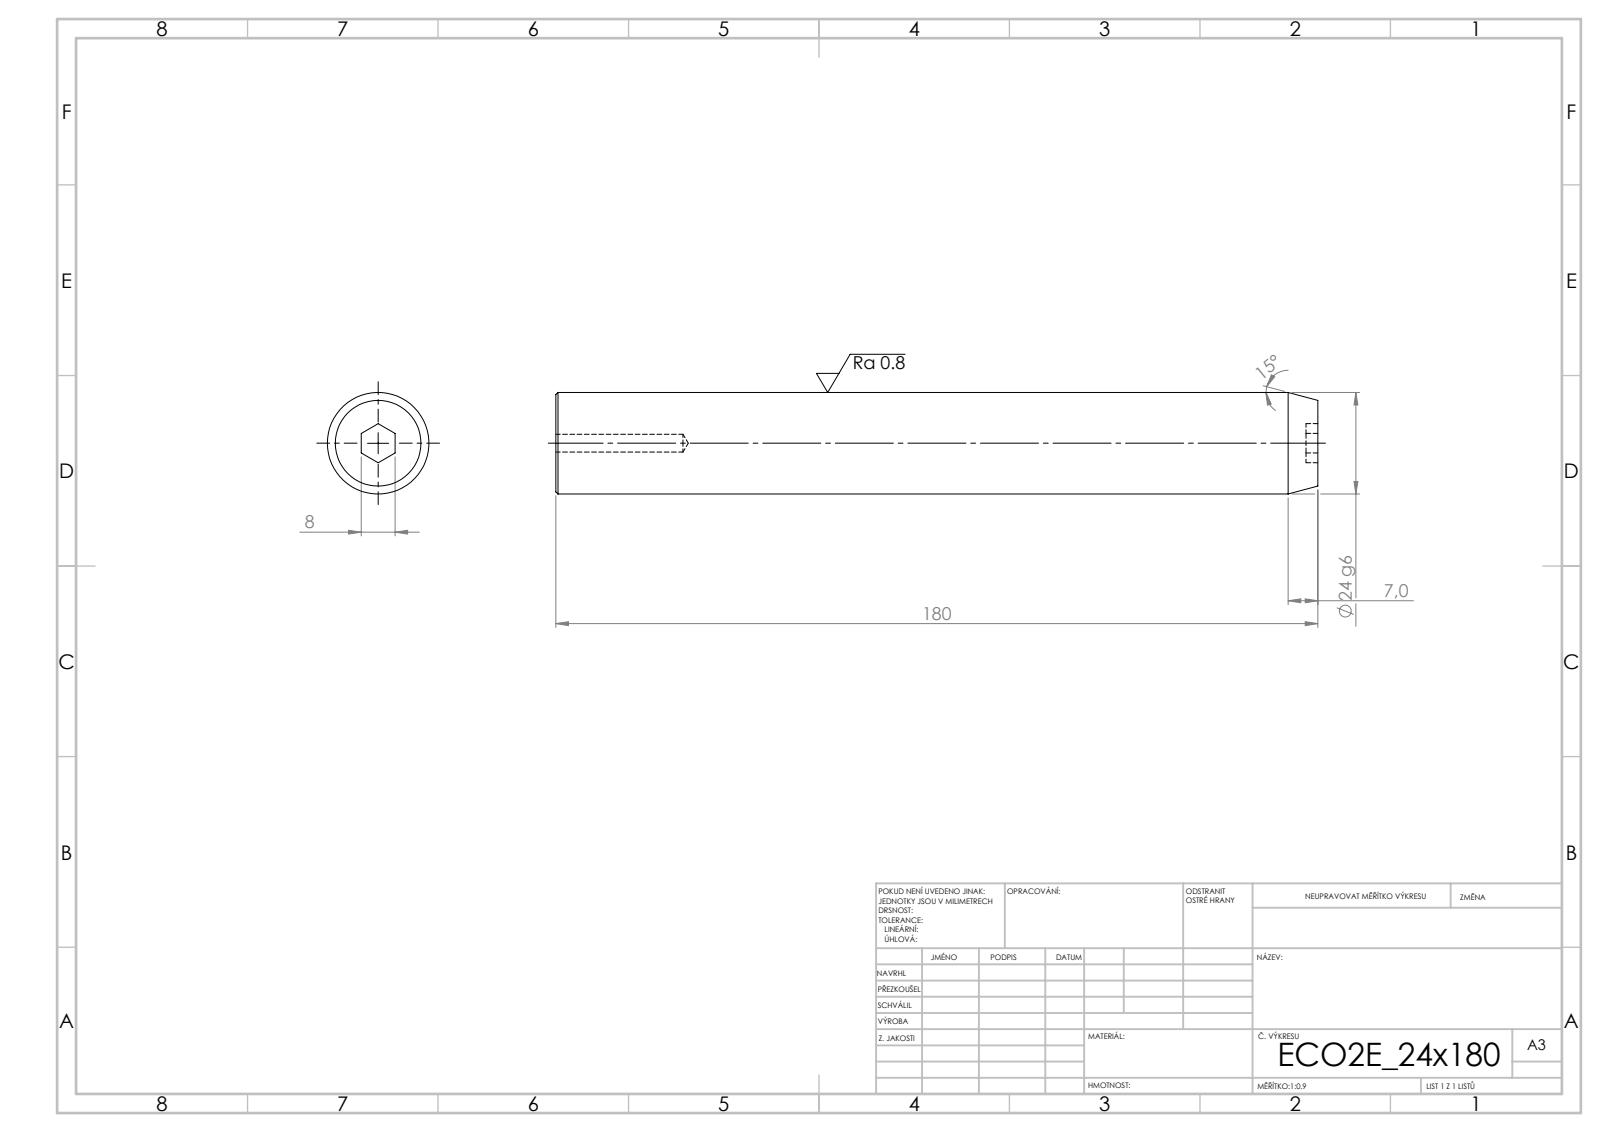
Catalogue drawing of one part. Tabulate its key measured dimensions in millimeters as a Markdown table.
| quantity | value |
| --- | --- |
| STEP written by | SolidWorks 2019 (CONFIG_CONTROL_DESIGN) |
| units | millimeters |
| bodies | 1 solid, 19 faces (9 planar, 4 cylindrical, 6 other) |
| overall size | 180 × 24 × 24 |
| volume | 80 375 mm³ |
| surface area | 14 775 mm² |
| round holes (diameter × count) | 4.2 × 1 |
| round bosses / shafts (diameter × count) | 24 × 1 |
| main face-to-face distances | 180, 2.8, 177.2, 8 |
